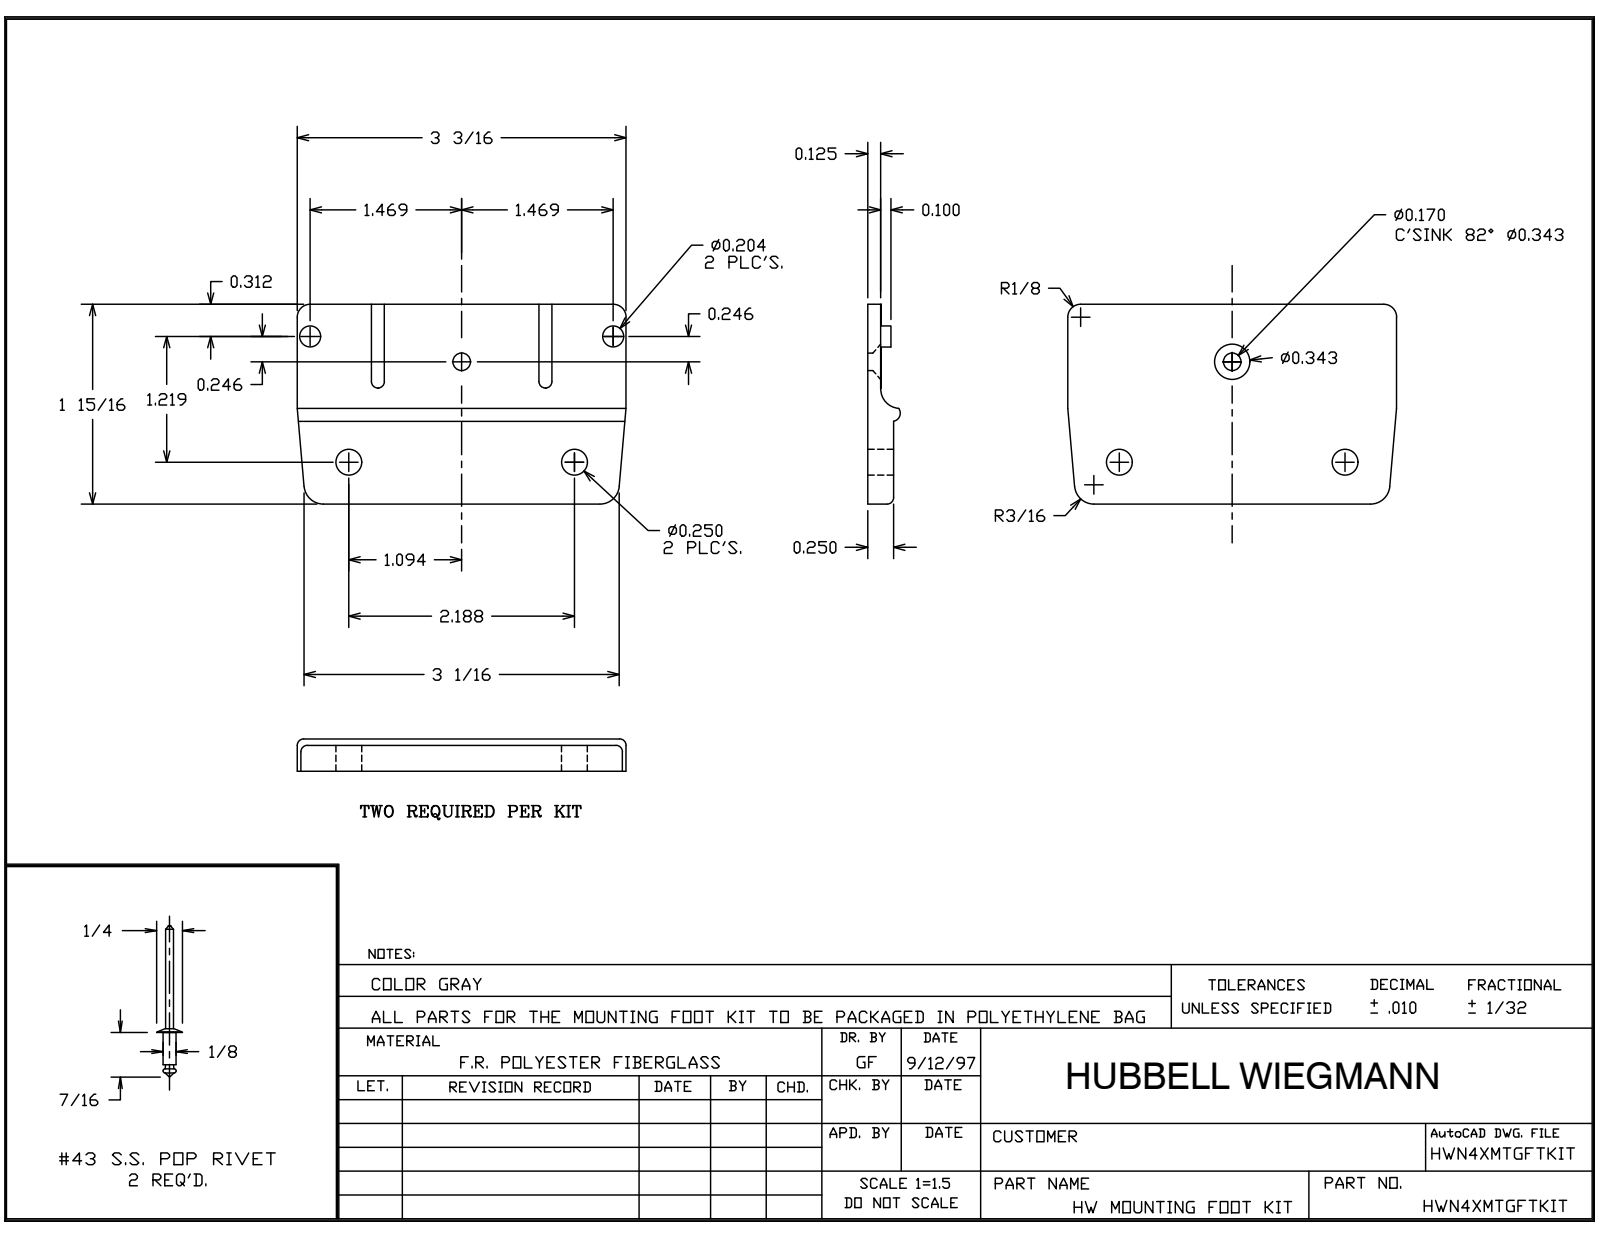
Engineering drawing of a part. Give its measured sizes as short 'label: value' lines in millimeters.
name: CFMTGFTKIT_STP
written by: Autodesk Inventor 2014 (AUTOMOTIVE_DESIGN)
unit: mm
bodies: 1 solid, 31 faces (18 planar, 12 cylindrical, 1 other)
size: 80.96 × 49.21 × 7.93
volume: 18 704 mm³; area: 9 563 mm²
holes: 2× ⌀6.35, 1× ⌀4.19
bosses: 2× ⌀5.33
rounds: 2× R1.59, 2× R4.76, 1× R1.59, 1× R4.78
face distances: 6.36, 3.17, 3.19, 49.21, 3.42, 2.94, 80.96, 5.46, 2.29, 2.04
hole spacings: 37.09, 55.56
